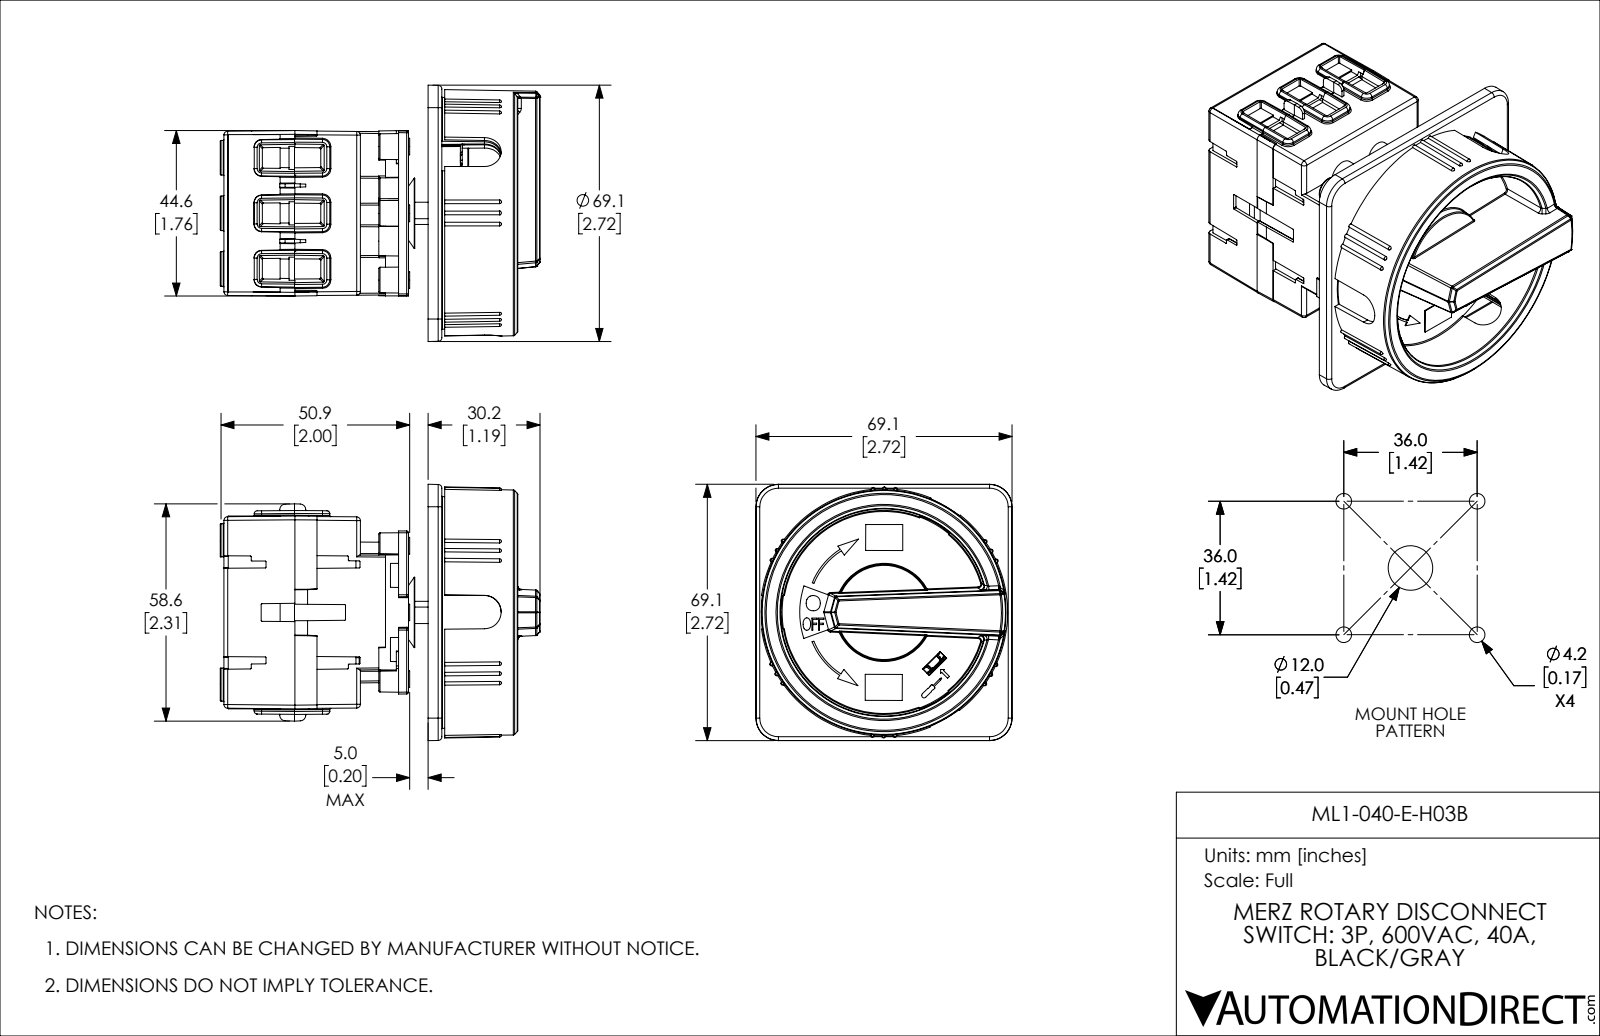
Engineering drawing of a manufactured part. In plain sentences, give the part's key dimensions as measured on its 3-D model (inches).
The part is named "ML1-040-E-H03B". Its 3-D file was written by "SolidWorks 2019 (AUTOMOTIVE_DESIGN)". It is 1 solid with 2964 faces: 1185 planar, 610 cylindrical and 1169 other. Overall it measures 3.398 by 2.722 by 2.722 inches. Its volume is 8.361 cubic inches and its surface area 101.4 square inches. Round bosses or shafts: 2 of diameter 0.071, 1 of diameter 0.748, 1 of diameter 0.236. Partial cylindrical surfaces (rounded edges, fillets, slot ends): 132 of radius 0.02, 68 of radius 0.012, 50 of radius 0.039, 44 of radius 0.008, 41 of radius 0.008, 39 of radius 0.01, 34 of radius 0.031, 12 of radius 0.079. The main face-to-face distances are 0.059, 0.138, 0.197, 0.079, 0.276, 0.571, 0.02, 0.551, 0.295, 0.807.
